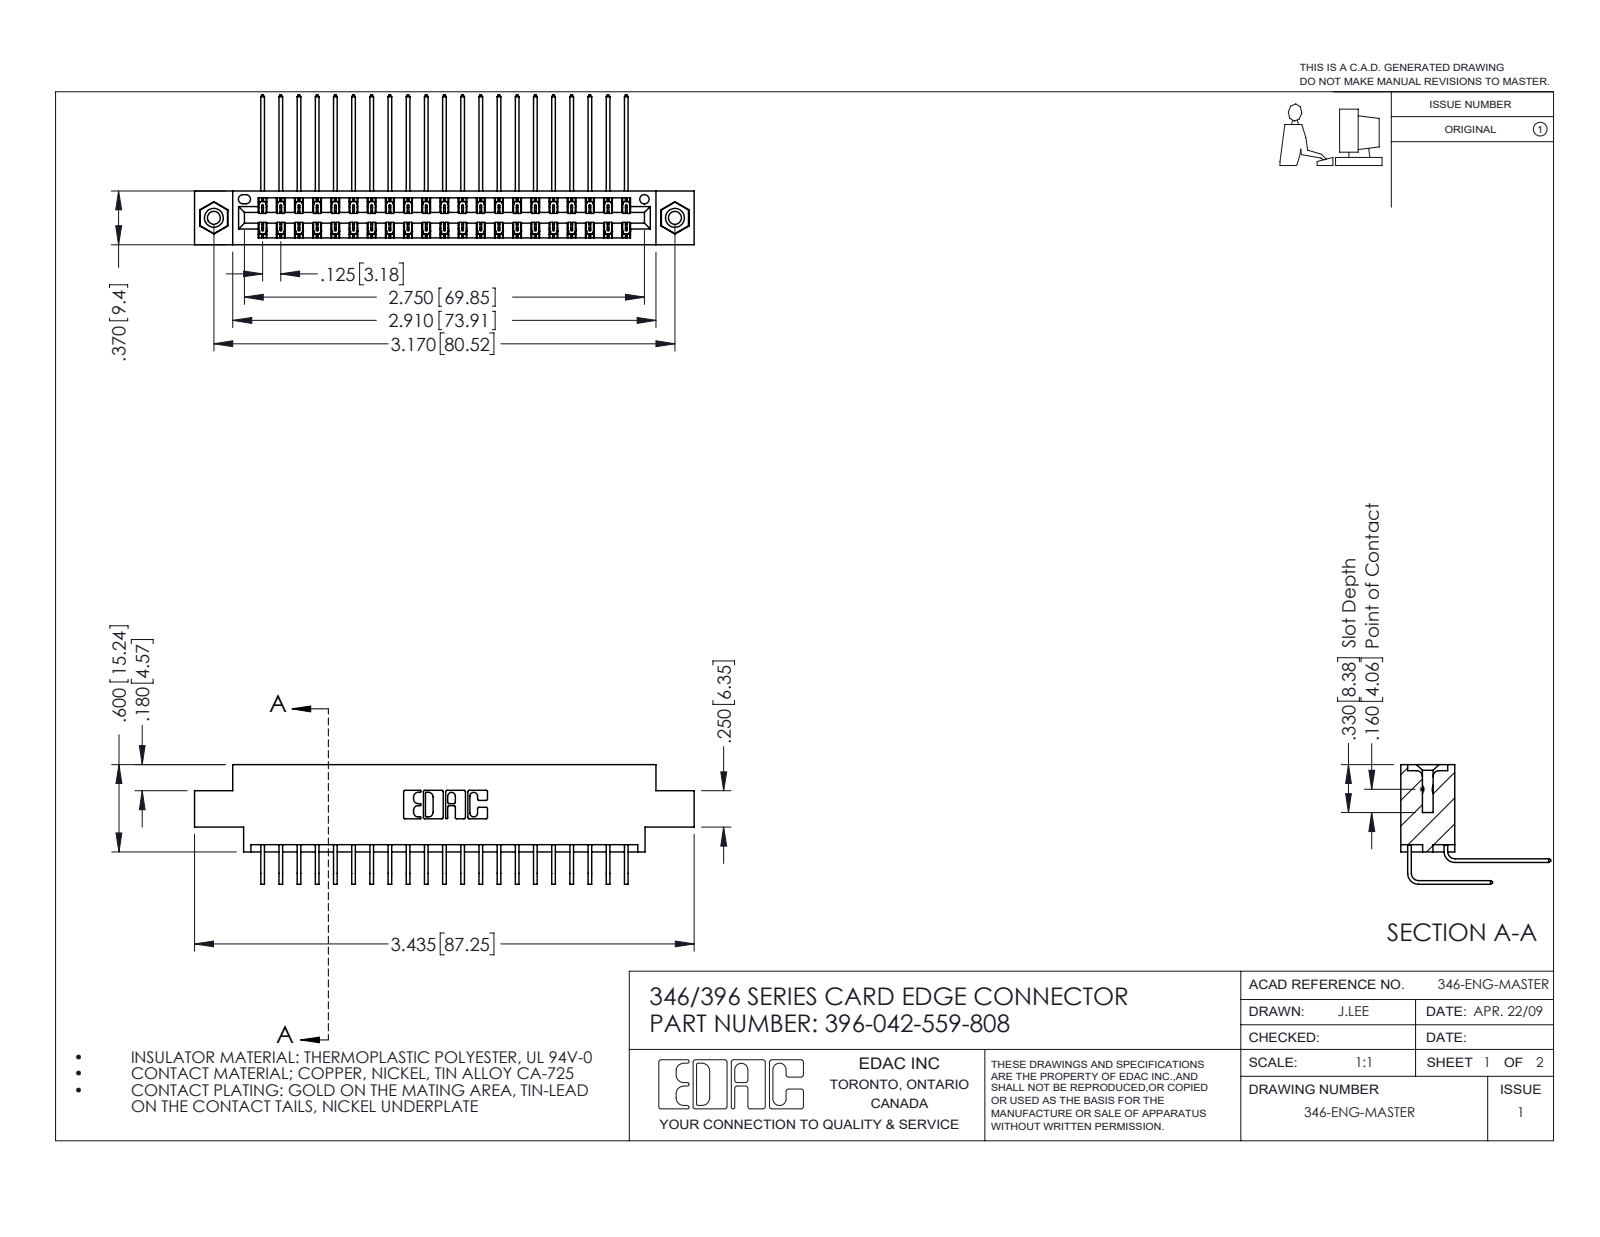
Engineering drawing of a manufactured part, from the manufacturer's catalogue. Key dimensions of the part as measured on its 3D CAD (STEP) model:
Part name (STEP PRODUCT): 396-042-559-808; 345-292-001_558 559 Tail - 1; 345-292-001_559 Tail - 2; 346 Part_0.170 Offset - 0.156 Dia-TI (+1 more)
STEP written by: SolidWorks 2016 (CONFIG_CONTROL_DESIGN)
Units: inches
Bodies: 45 solids, 2454 faces (1666 planar, 772 cylindrical, 16 other)
Overall size (bounding box): 3.435 × 1.03 × 0.823
Volume: 0.514 in³ · Surface area: 19.55 in²
Round holes (diameter × count): ⌀0.089 ×2, ⌀0.125 ×2, ⌀0.156 ×2, ⌀0.064 ×1
Round bosses / shafts (diameter × count): ⌀0.155 ×2
Partial cylindrical surfaces — rounded edges, fillets, slot ends (radius × count): R0.006 ×63, R0.01 ×22, R0.007 ×6, R0.031 ×6, R0.026 ×3, R0.014 ×2, R0.022 ×2, R0.024 ×2
Main face-to-face distances: 0.048, 0.322, 0.37, 0.025, 0.25, 0.072, 0.298, 0.275, 0.222, 0.148
Hole centre spacings: 0.246, 2.963, 3.17
